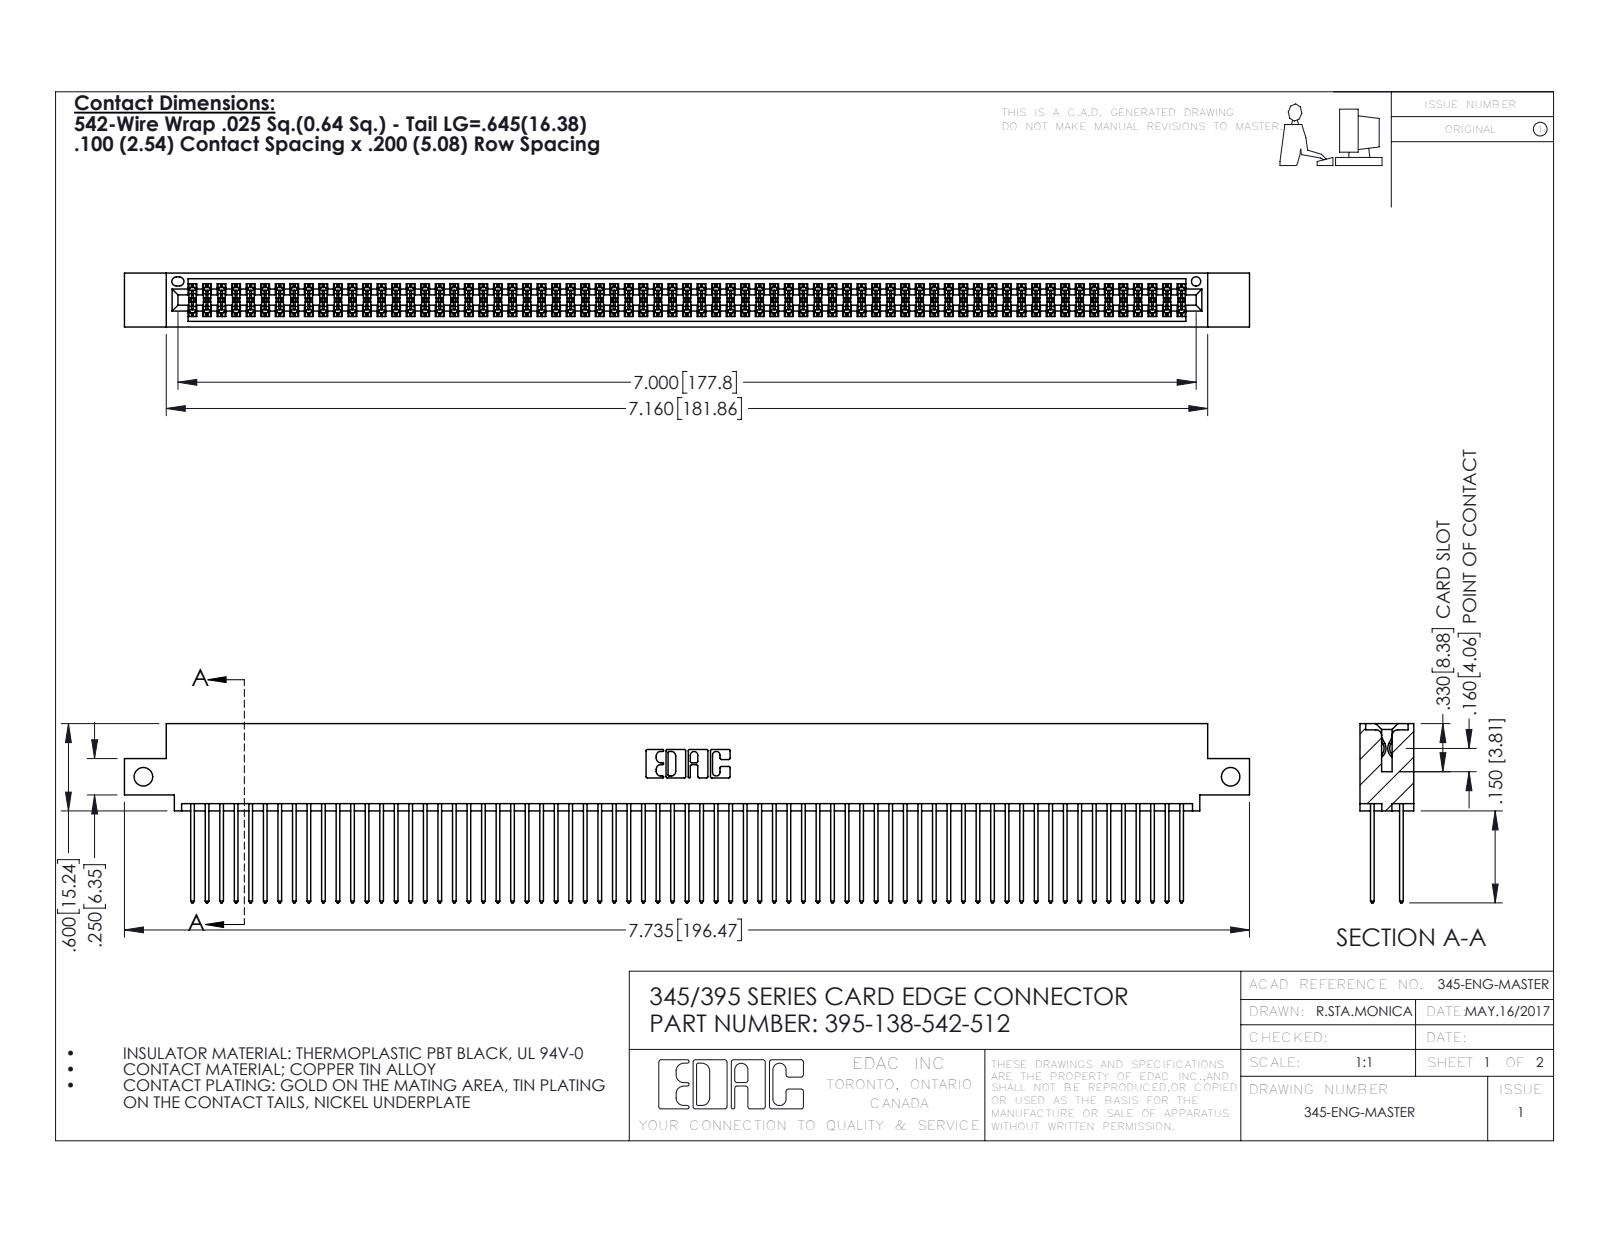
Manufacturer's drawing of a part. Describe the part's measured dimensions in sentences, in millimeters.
The part is named "345-292-001_345-293-142; 395-138-542-512; 345 Part_0.110 Offset - Side Mount". Its 3-D file was written by "SolidWorks 2016 (CONFIG_CONTROL_DESIGN)". It is 139 solids with 7030 faces: 4638 planar, 2392 cylindrical and 0 other. Overall it measures 196.5 by 31.3 by 9.4 millimeters. Its volume is 19 810 cubic millimeters and its surface area 32 780 square millimeters. Round holes: 2 of diameter 3.3, 1 of diameter 1.6. Partial cylindrical surfaces (rounded edges, fillets, slot ends): 207 of radius 0.2, 138 of radius 0.3, 22 of radius 0.3, 6 of radius 0.2, 6 of radius 0.8, 3 of radius 0.7, 2 of radius 0.4, 2 of radius 0.5. The main face-to-face distances are 1.8, 7.6, 5.1, 2.5, 6.9, 0.6, 5.7, 9.4, 4.4, 3.8. The hole center spacings are 189.9.
